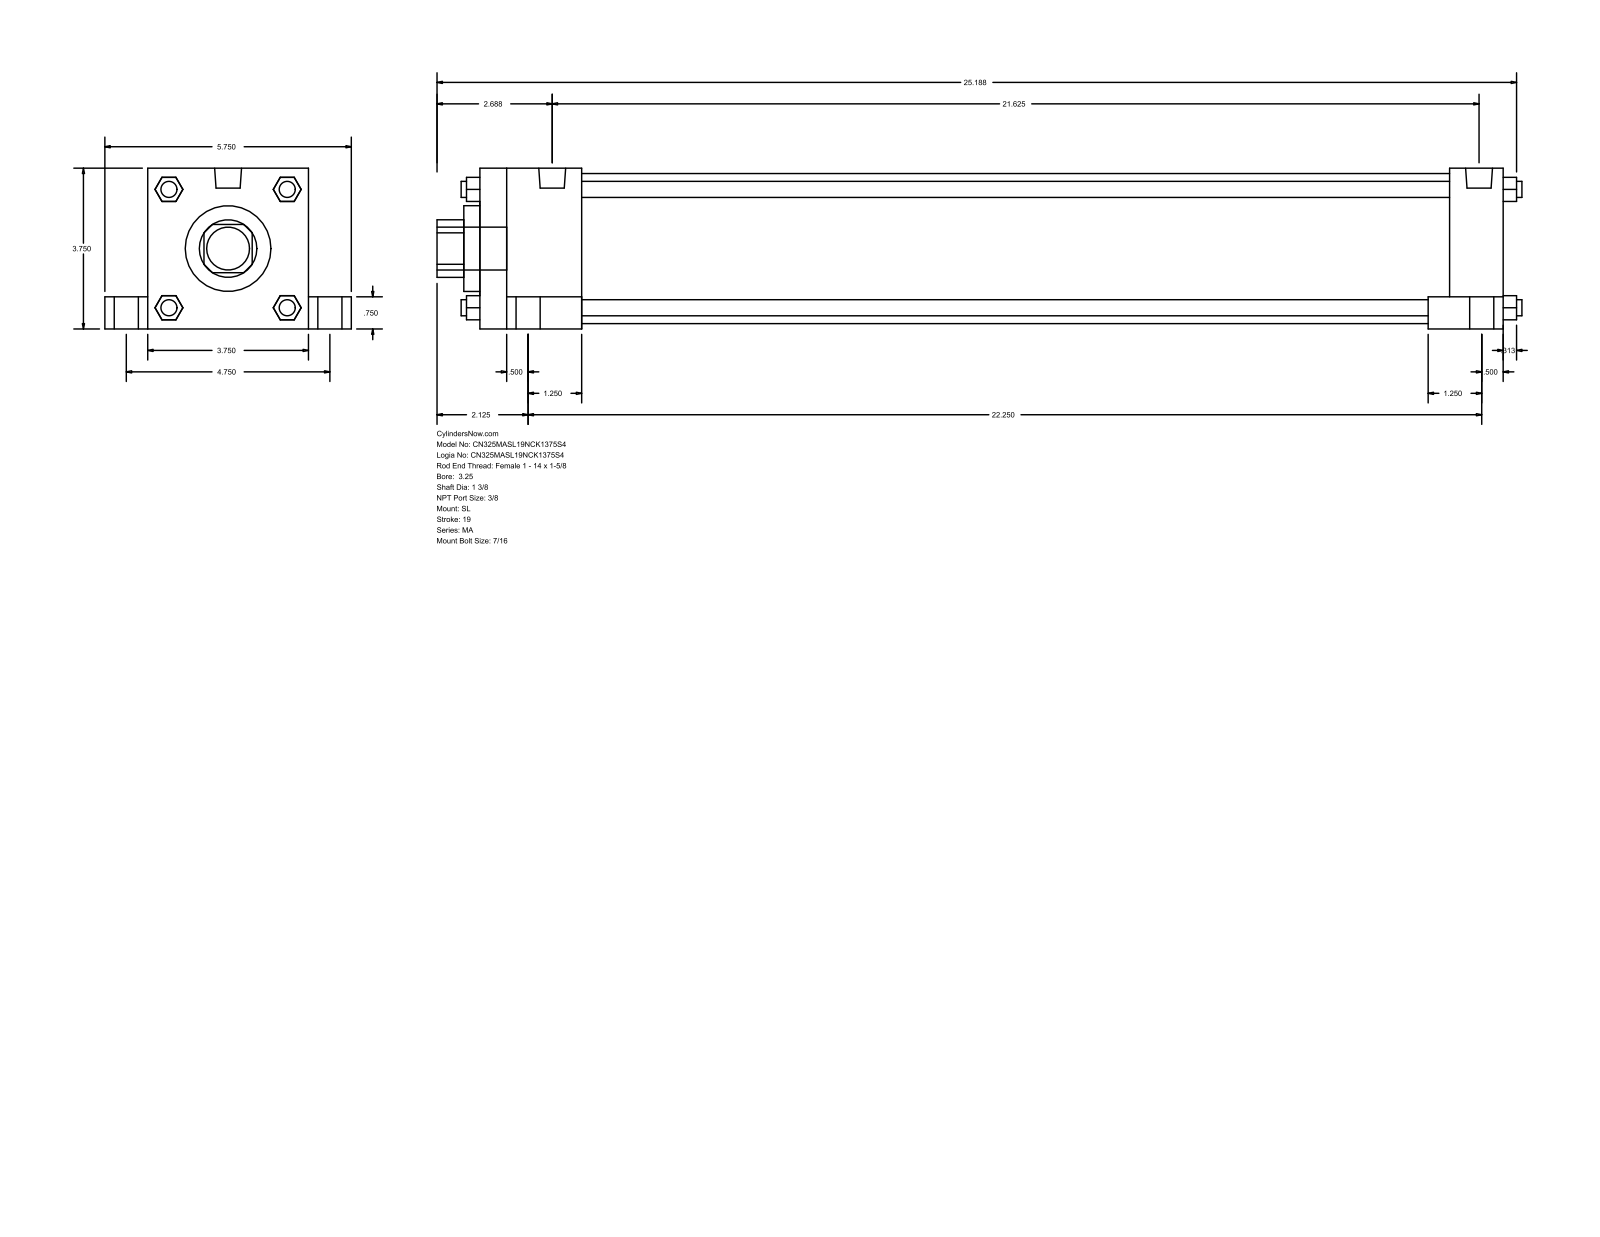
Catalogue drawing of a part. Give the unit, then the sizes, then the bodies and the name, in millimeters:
Units: millimetres
Overall size (bounding box): 642.94 × 146.05 × 95.25
Round holes (diameter × count): ⌀34.92 ×1, ⌀50.8 ×1, ⌀88.9 ×1
Round bosses / shafts (diameter × count): ⌀20.64 ×4, ⌀14.29 ×4, ⌀11.11 ×4, ⌀9.53 ×4, ⌀15.93 ×2, ⌀25.4 ×1
Partial cylindrical surfaces — rounded edges, fillets, slot ends (radius × count): R17.06 ×1
Main face-to-face distances: 95.24, 606.43, 25.41, 120.65, 574.68, 31.75, 60.32, 514.36, 546.11, 19.05
Bodies: 0 solids, 148 faces (112 planar, 36 cylindrical, 0 other)
Part name (STEP PRODUCT): MA_SL__0325_1.375
STEP written by: GSSL Pune (CONFIG_CONTROL_DESIGN)
